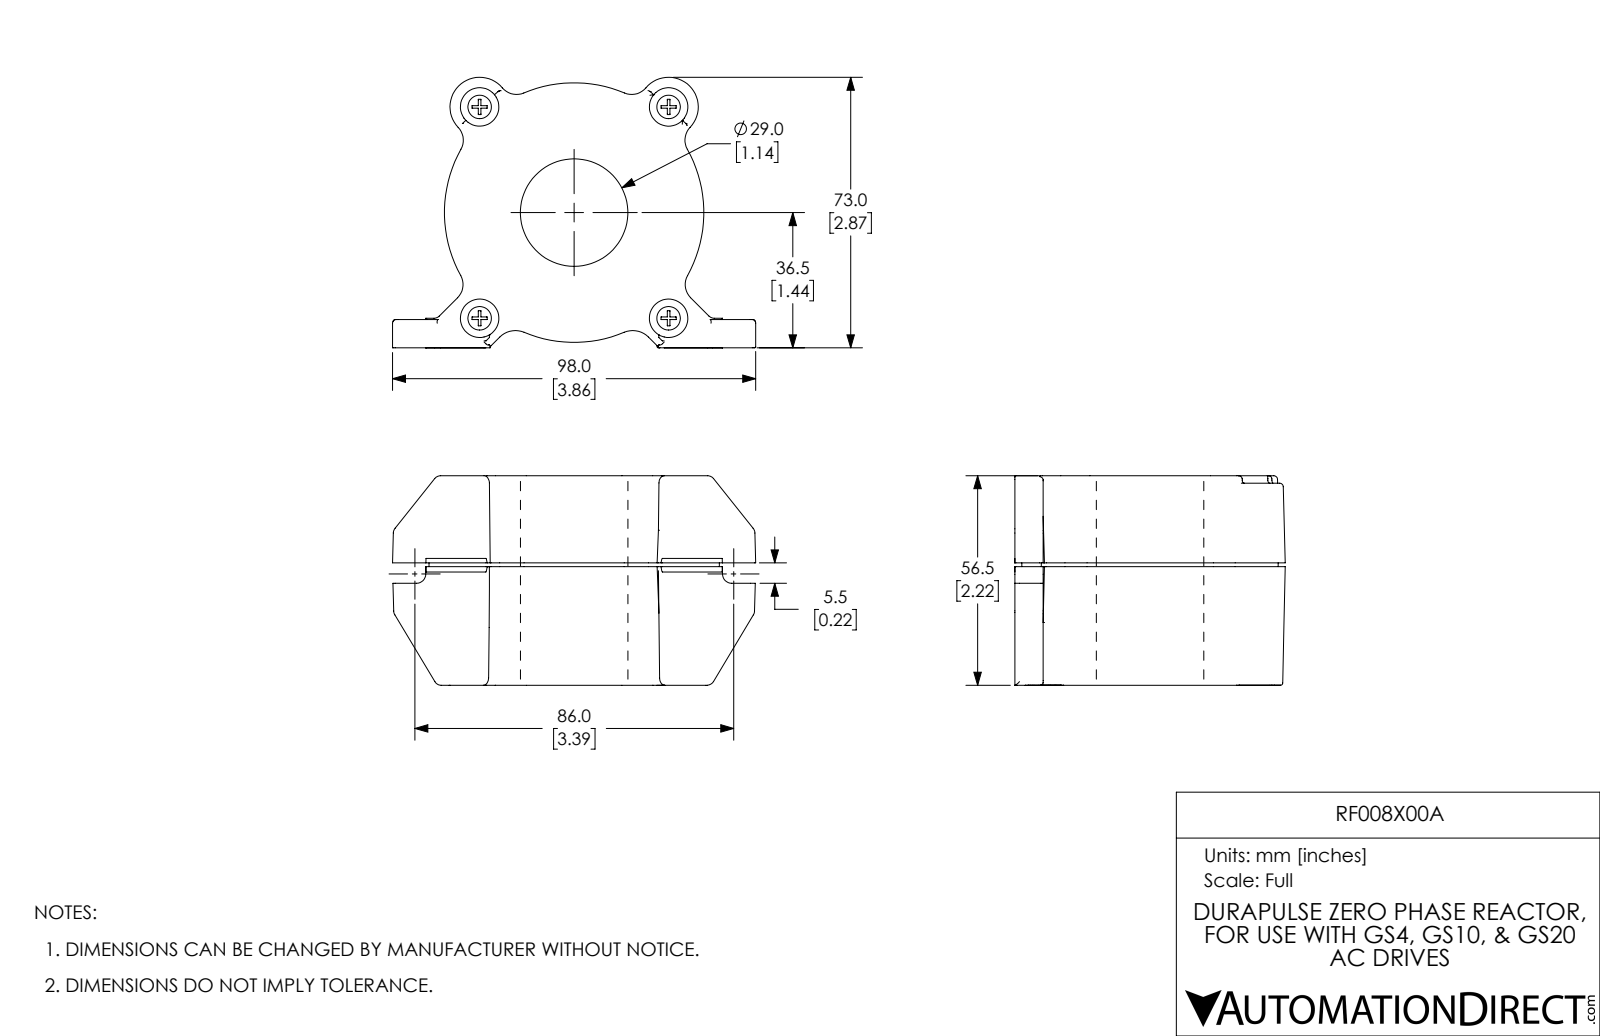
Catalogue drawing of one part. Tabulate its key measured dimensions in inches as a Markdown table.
| quantity | value |
| --- | --- |
| part name | RF008X00A |
| STEP written by | SolidWorks 2017 (AUTOMOTIVE_DESIGN) |
| units | inches |
| bodies | 1 solid, 489 faces (156 planar, 149 cylindrical, 184 other) |
| overall size | 3.858 × 2.84 × 2.216 |
| volume | 13 in³ |
| surface area | 51.87 in² |
| round holes (diameter × count) | 0.409 × 2, 0.424 × 1, 0.426 × 1, 1.142 × 1, 1.342 × 1 |
| round bosses / shafts (diameter × count) | 0.409 × 2, 1.169 × 1 |
| partial cylindrical surfaces (radius × count) | 0.049 × 22, 0.039 × 14, 0.01 × 8, 0.272 × 6, 0.03 × 4, 0.079 × 4, 0.087 × 4, 0.229 × 4 |
| main face-to-face distances | 2.216, 0.301, 1.293, 0.923, 1.254, 0.039, 0.962, 2.211, 0.957, 0.918 |
| hole center spacings | 1.506, 2.008, 2.244, 3.011 |
